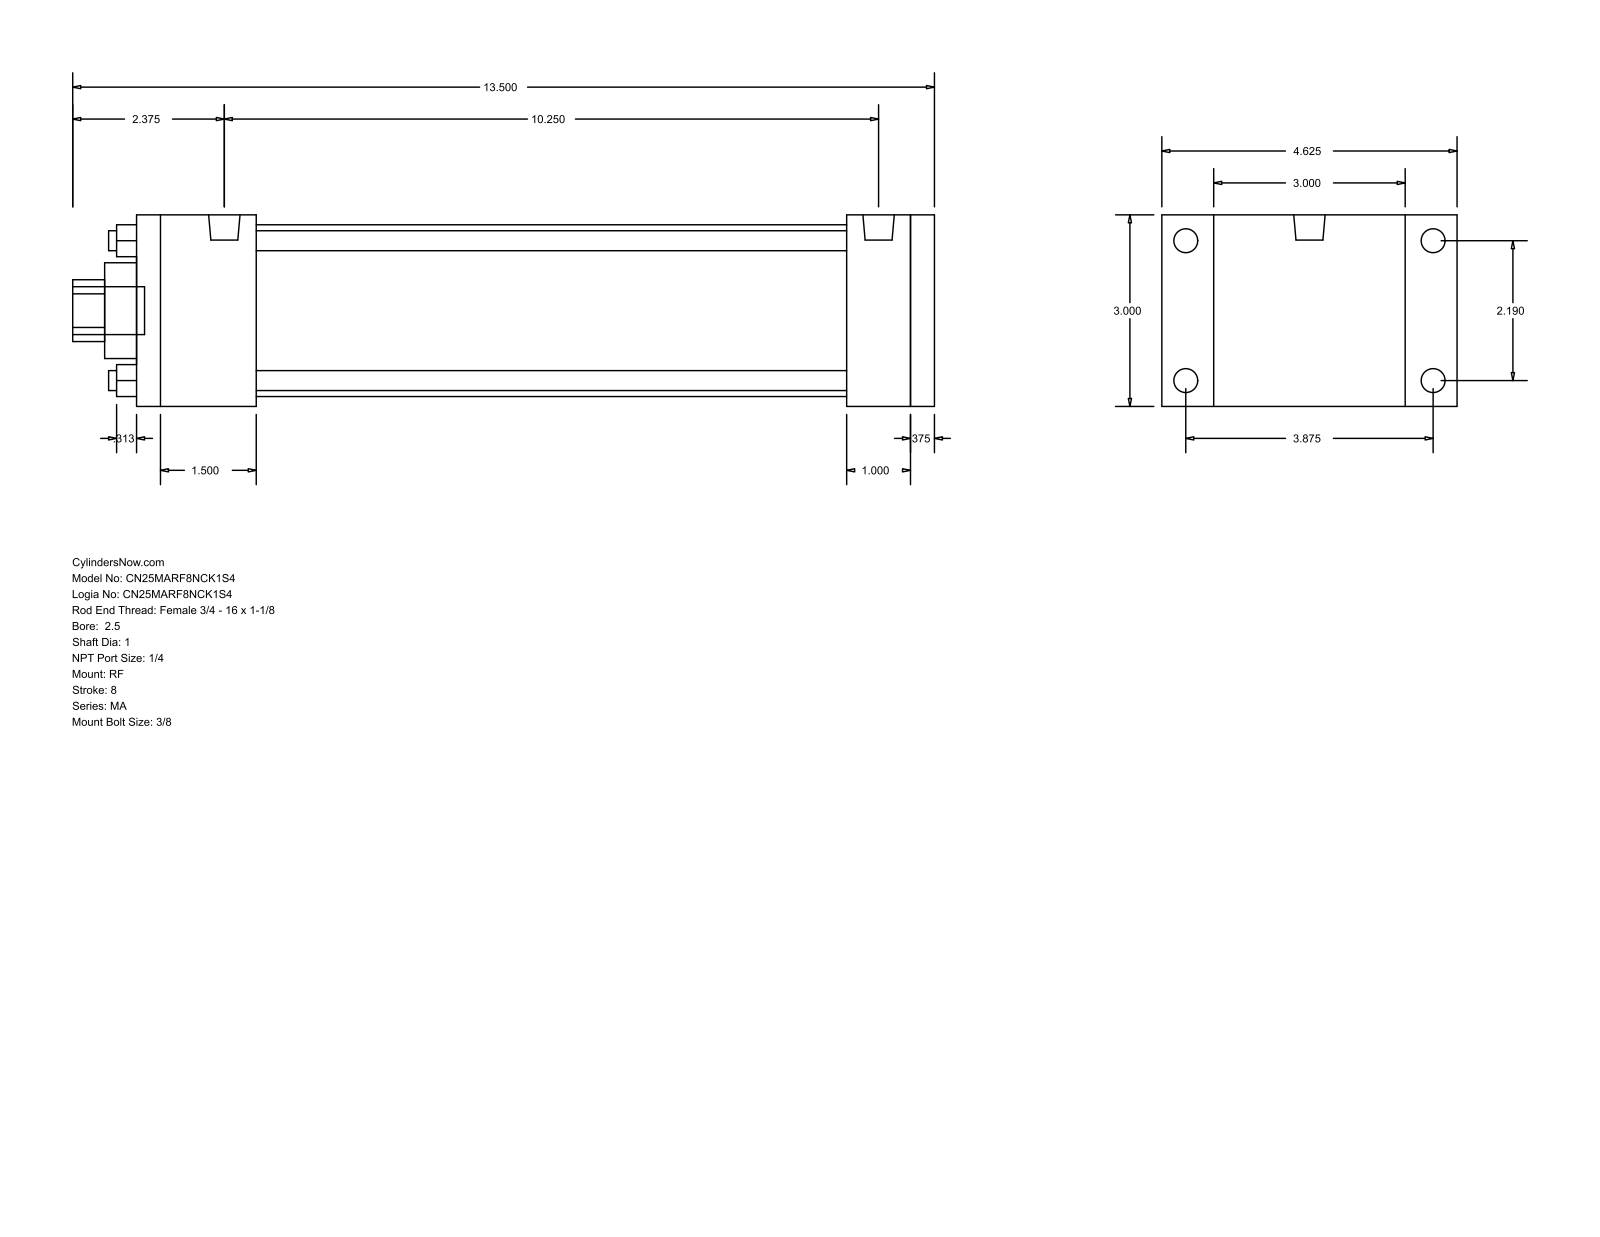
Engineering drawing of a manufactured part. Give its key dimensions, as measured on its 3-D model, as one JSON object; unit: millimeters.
{"part_name": "MA_RF__0250_1", "step_written_by": "GSSL Pune (CONFIG_CONTROL_DESIGN)", "units": "millimeters", "bodies": {"solids": 0, "faces": 92, "planar": 64, "cylindrical": 28, "other": 0}, "overall_size": [342.9, 117.47, 76.2], "round_holes": [[7.94, 4], [25.4, 1], [38.1, 1], [68.33, 1]], "round_bosses_or_shafts": [[9.53, 4], [7.94, 4], [12.49, 2], [19.05, 1]], "partial_cylinders_radius": [[12.29, 1]], "face_to_face_distances": [76.2, 317.5, 307.98, 9.52, 25.4, 47.63, 282.58, 234.95, 260.35, 269.87], "hole_center_spacings": [39.33, 55.62, 78.66]}
